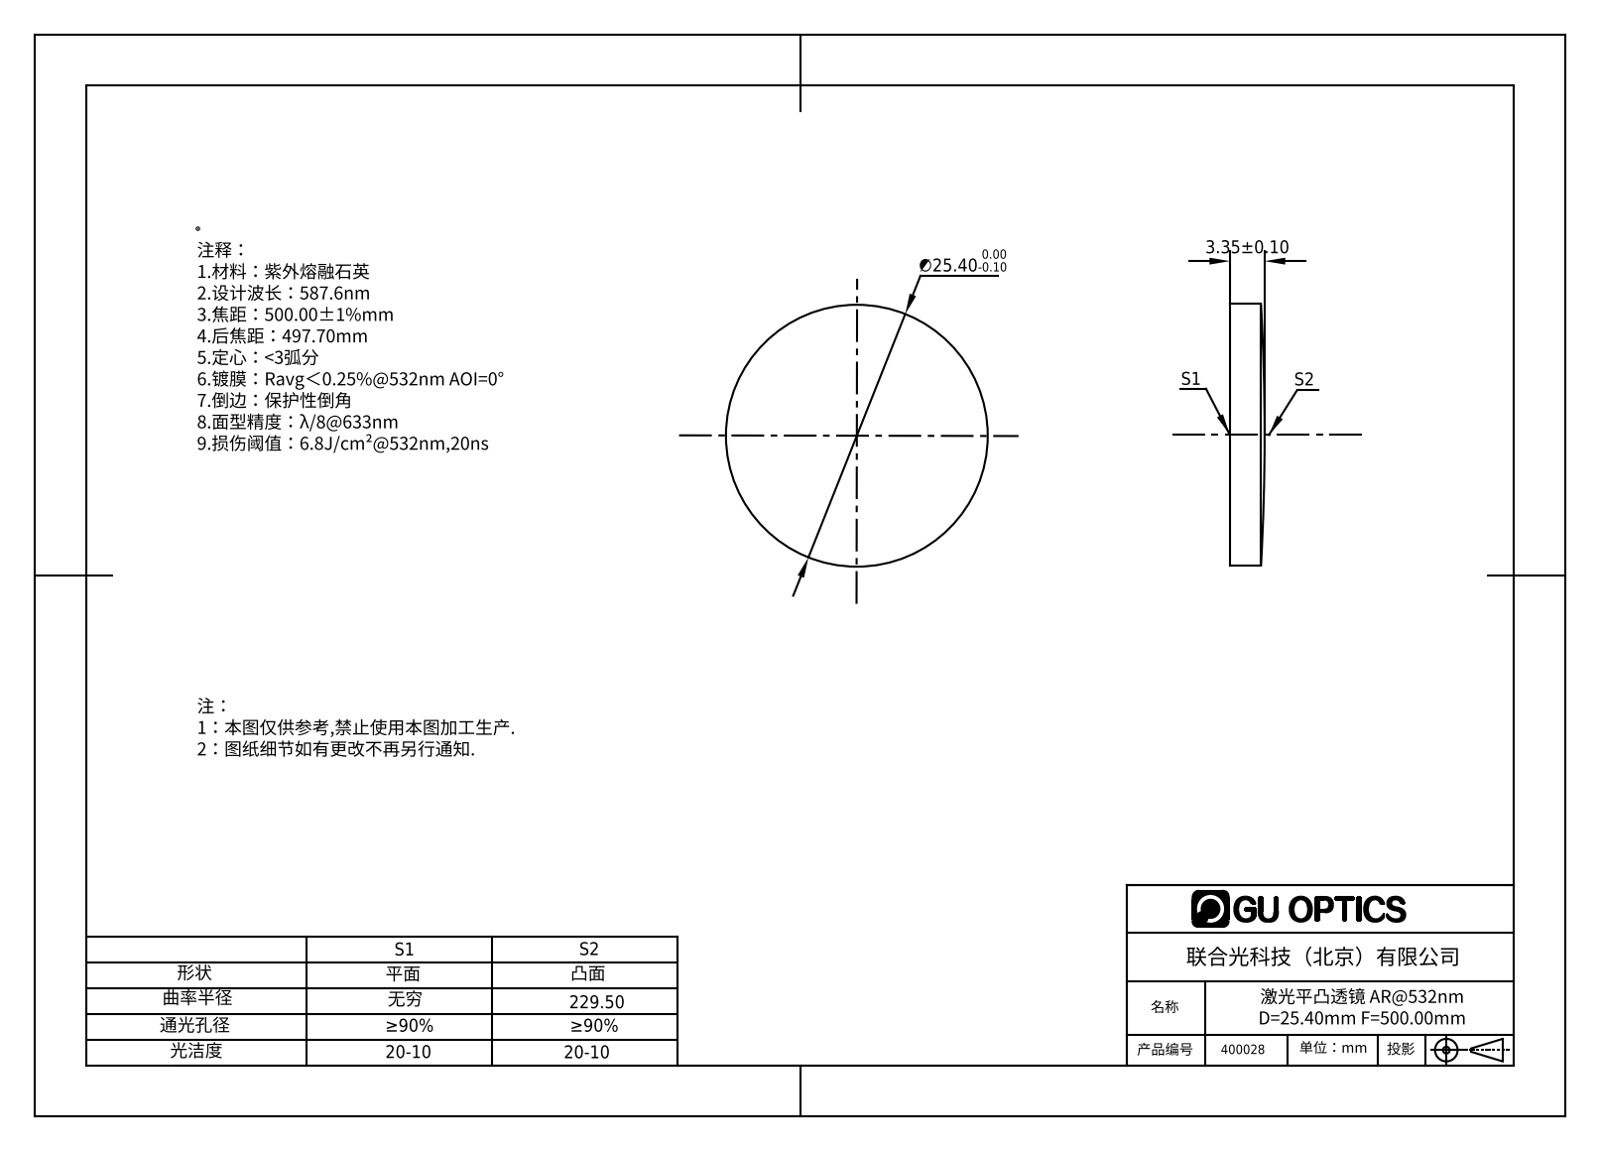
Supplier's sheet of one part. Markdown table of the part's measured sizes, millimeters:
| quantity | value |
| --- | --- |
| part name | 400021 |
| STEP written by | SolidWorks 2016 (AUTOMOTIVE_DESIGN) |
| units | millimeters |
| bodies | 1 solid, 5 faces (1 planar, 2 cylindrical, 2 other) |
| overall size | 25.4 × 25.4 × 3.35 |
| volume | 1 609 mm³ |
| surface area | 1 253 mm² |
| round bosses / shafts (diameter × count) | 25.4 × 1 |
